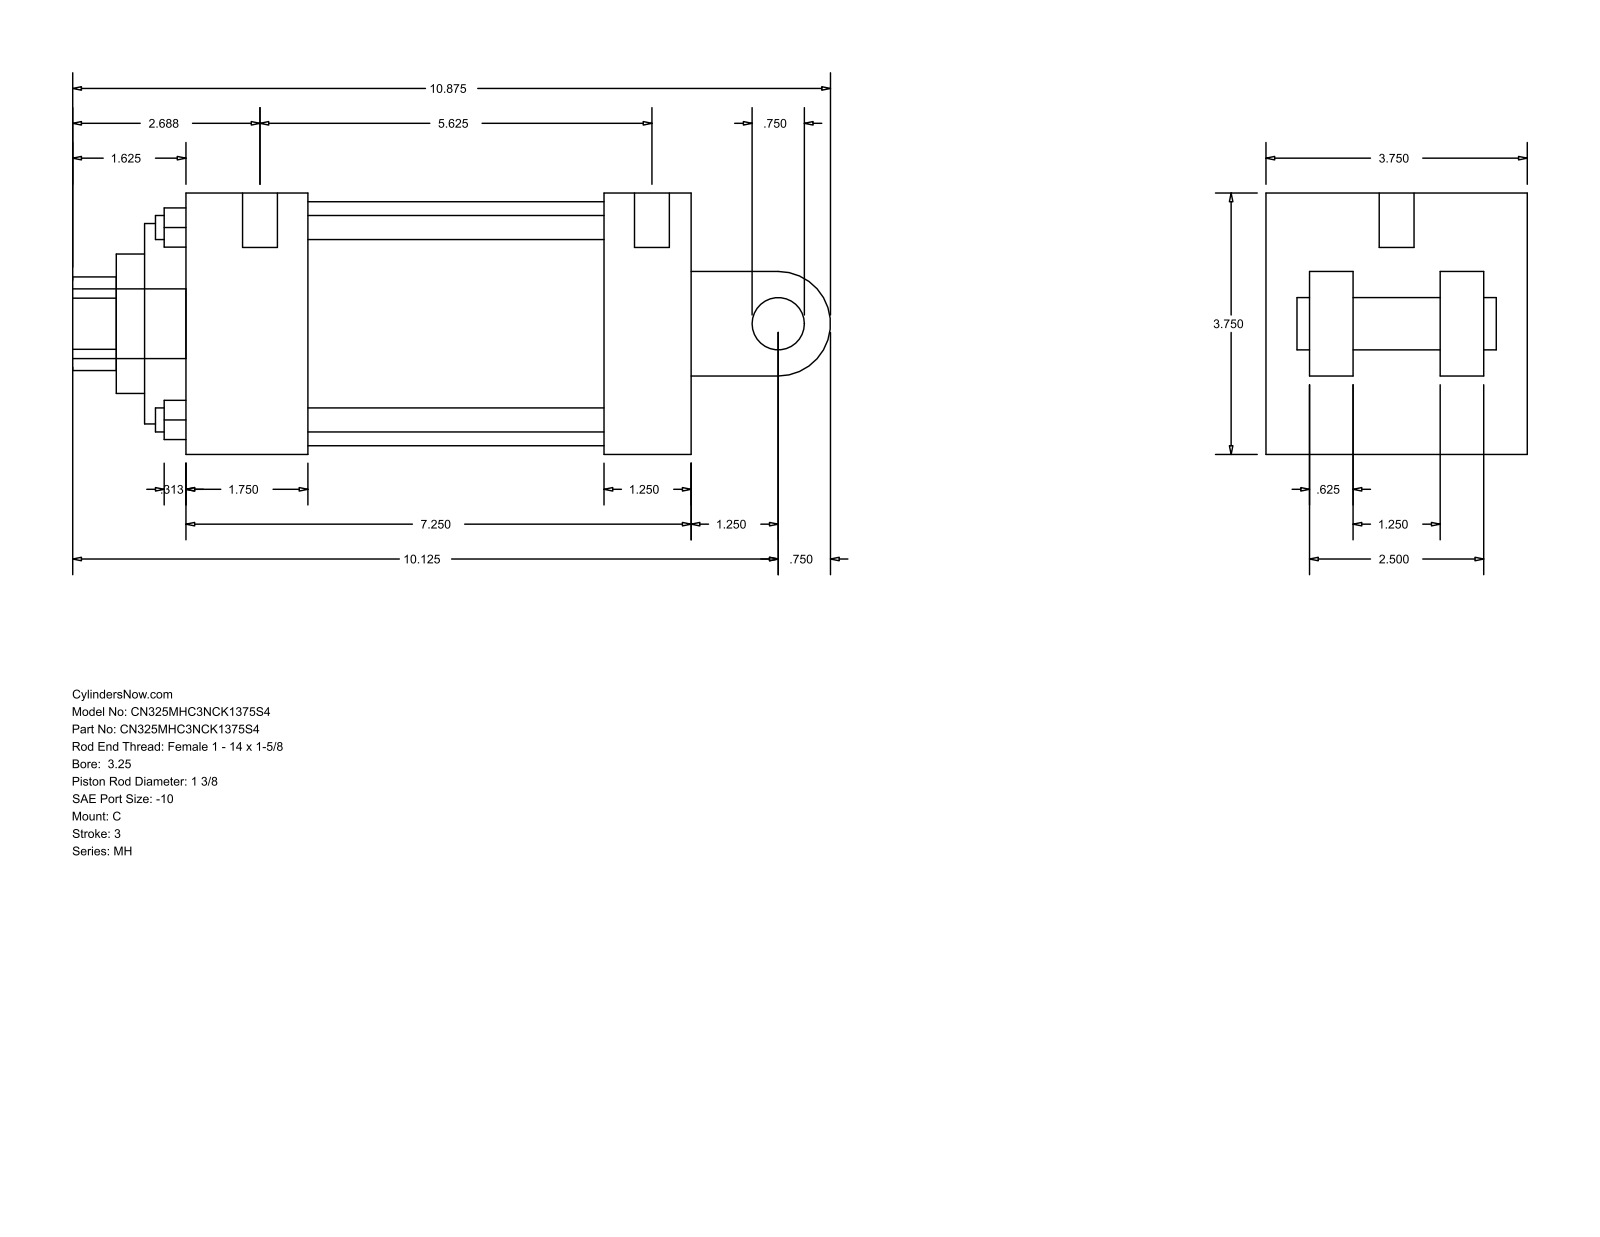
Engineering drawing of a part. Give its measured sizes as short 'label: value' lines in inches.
name: MH_C__0325_1.375
written by: GSSL Pune (CONFIG_CONTROL_DESIGN)
unit: in
bodies: 0 solids, 101 faces (71 planar, 30 cylindrical, 0 other)
size: 10.875 × 3.75 × 3.75
holes: 4× ⌀0.345, 2× ⌀0.219, 1× ⌀0.5, 1× ⌀1.375, 1× ⌀2, 1× ⌀2.875, 1× ⌀3.5
bosses: 2× ⌀0.219, 1× ⌀1, 1× ⌀0.75, 1× ⌀0.5
rounds: 1× R0.672, 1× R0.75
face distances: 3.75, 0.625, 7.25, 2.5, 1.25, 3.125, 1.875, 1.75, 6, 4.25
hole spacings: 1.952, 2.76, 3.903, 0.187
